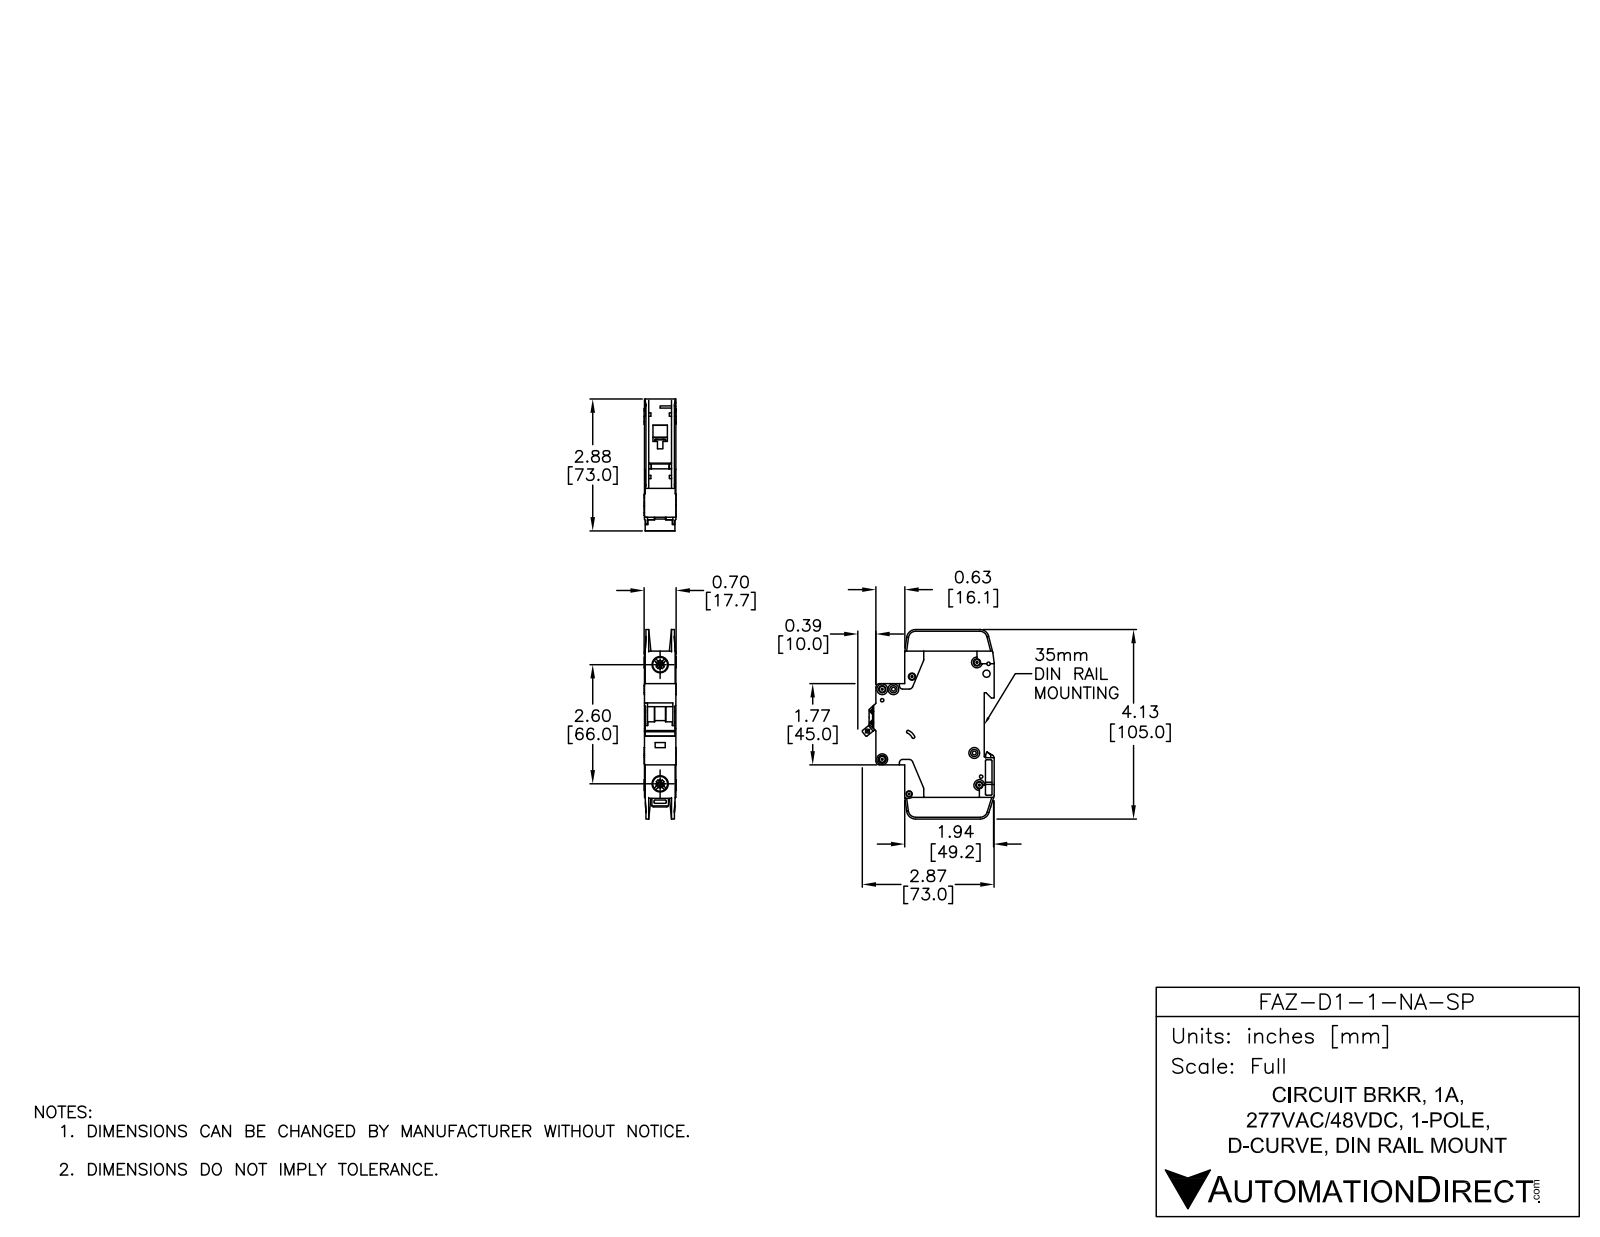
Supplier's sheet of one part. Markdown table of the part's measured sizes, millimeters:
| quantity | value |
| --- | --- |
| part name | FAZ-D1-1-NA-SP |
| STEP written by | SolidWorks 2014 (AUTOMOTIVE_DESIGN) |
| units | millimeters |
| bodies | 3 solids, 784 faces (409 planar, 263 cylindrical, 112 other) |
| overall size | 105 × 73.04 × 17.7 |
| volume | 77 695 mm³ |
| surface area | 24 740 mm² |
| round holes (diameter × count) | 3.6 × 7, 1.09 × 2, 1.5 × 2, 4 × 2, 7.15 × 2, 8.2 × 2, 1.9 × 1, 2.15 × 1, 2.2 × 1, 2.55 × 1, 3.3 × 1, 3.4 × 1 |
| round bosses / shafts (diameter × count) | 6 × 7, 2.5 × 1 |
| partial cylindrical surfaces (radius × count) | 0.25 × 29, 0.5 × 18, 1 × 10, 2 × 10, 5 × 5, 4 × 4, 1.8 × 3, 0.2 × 2 |
| main face-to-face distances | 17.5, 15.05, 0.7, 2.45, 1.75, 15.75, 13.3, 14, 12.6, 2 |
| hole center spacings | 6.2, 5.19, 6.1, 8.19, 8.56, 8.7, 11.11, 12.45 |
